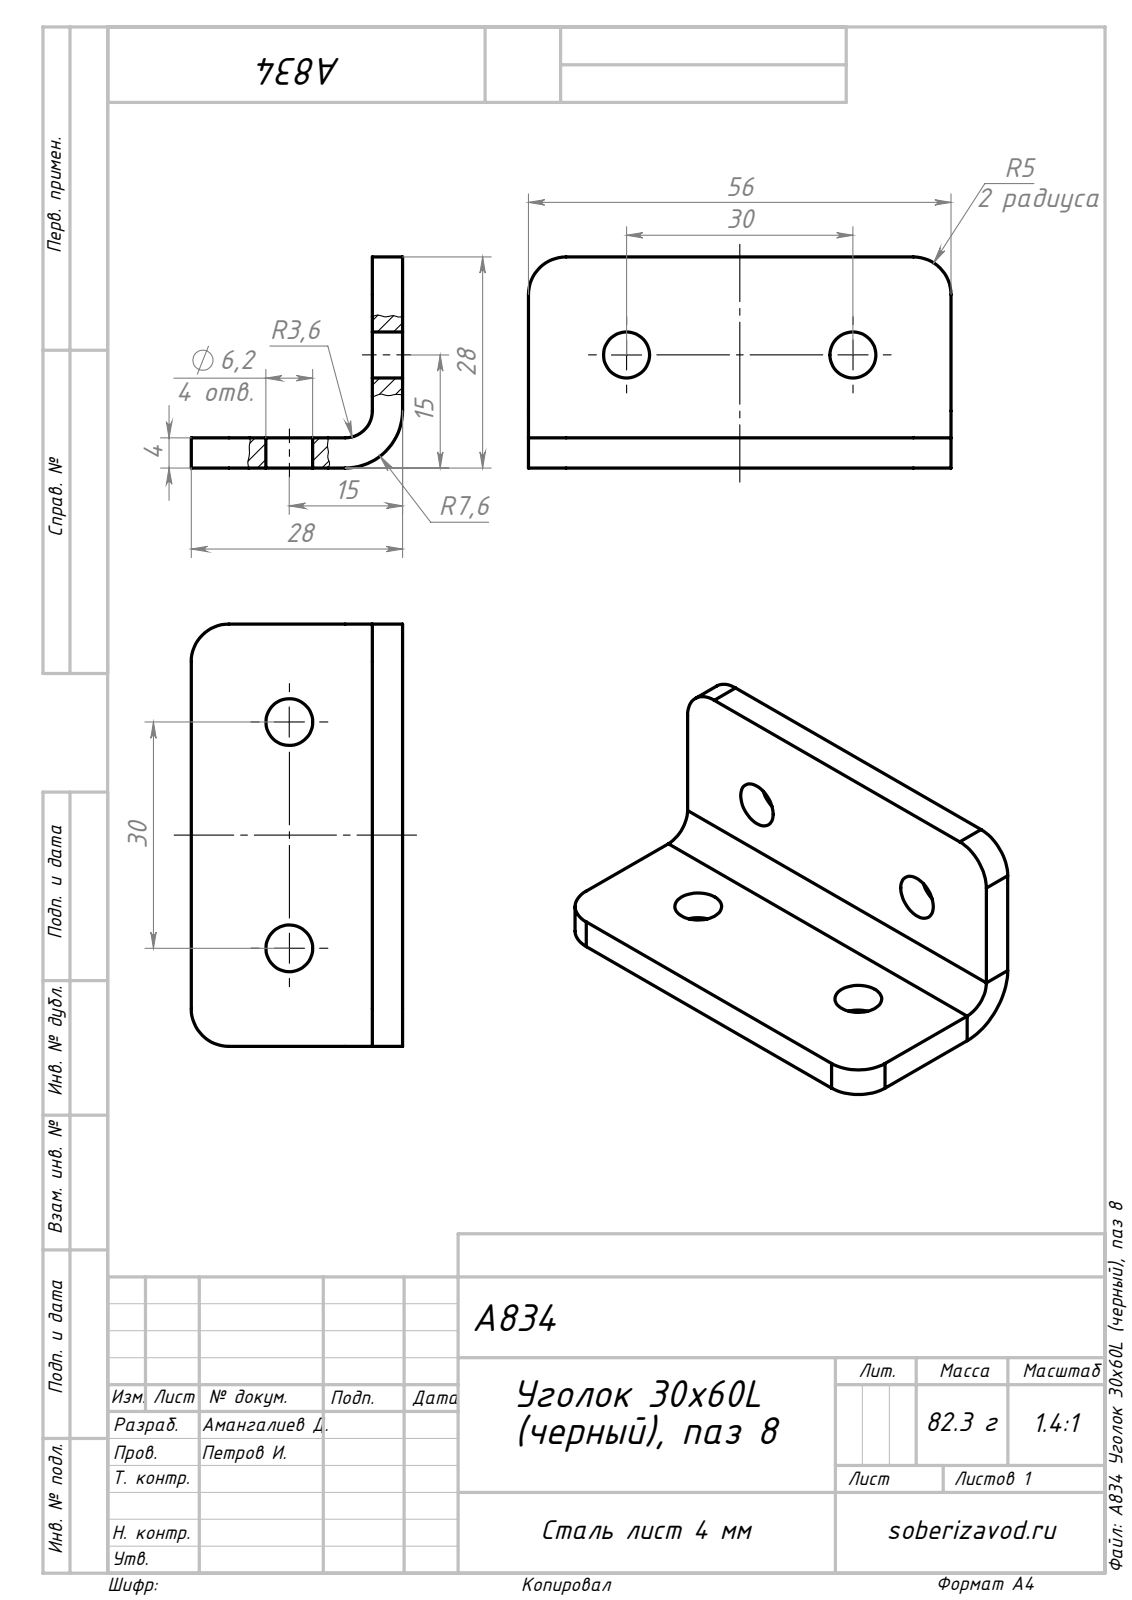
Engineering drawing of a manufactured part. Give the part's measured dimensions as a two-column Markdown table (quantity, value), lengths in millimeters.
| quantity | value |
| --- | --- |
| part name | Сборка2; A834 Уголок 30х60L (черный), паз 8_00 |
| STEP written by | SolidWorks 2022 (AUTOMOTIVE_DESIGN) |
| units | millimeters |
| bodies | 1 solid, 26 faces (12 planar, 14 cylindrical, 0 other) |
| overall size | 56 × 28 × 28 |
| volume | 10 548 mm³ |
| surface area | 6 394 mm² |
| round holes (diameter × count) | 6.1 × 2, 6.2 × 2 |
| partial cylindrical surfaces (radius × count) | 5 × 4, 3.6 × 1, 7.6 × 1 |
| main face-to-face distances | 4, 28, 24, 56 |
| hole center spacings | 30 |
